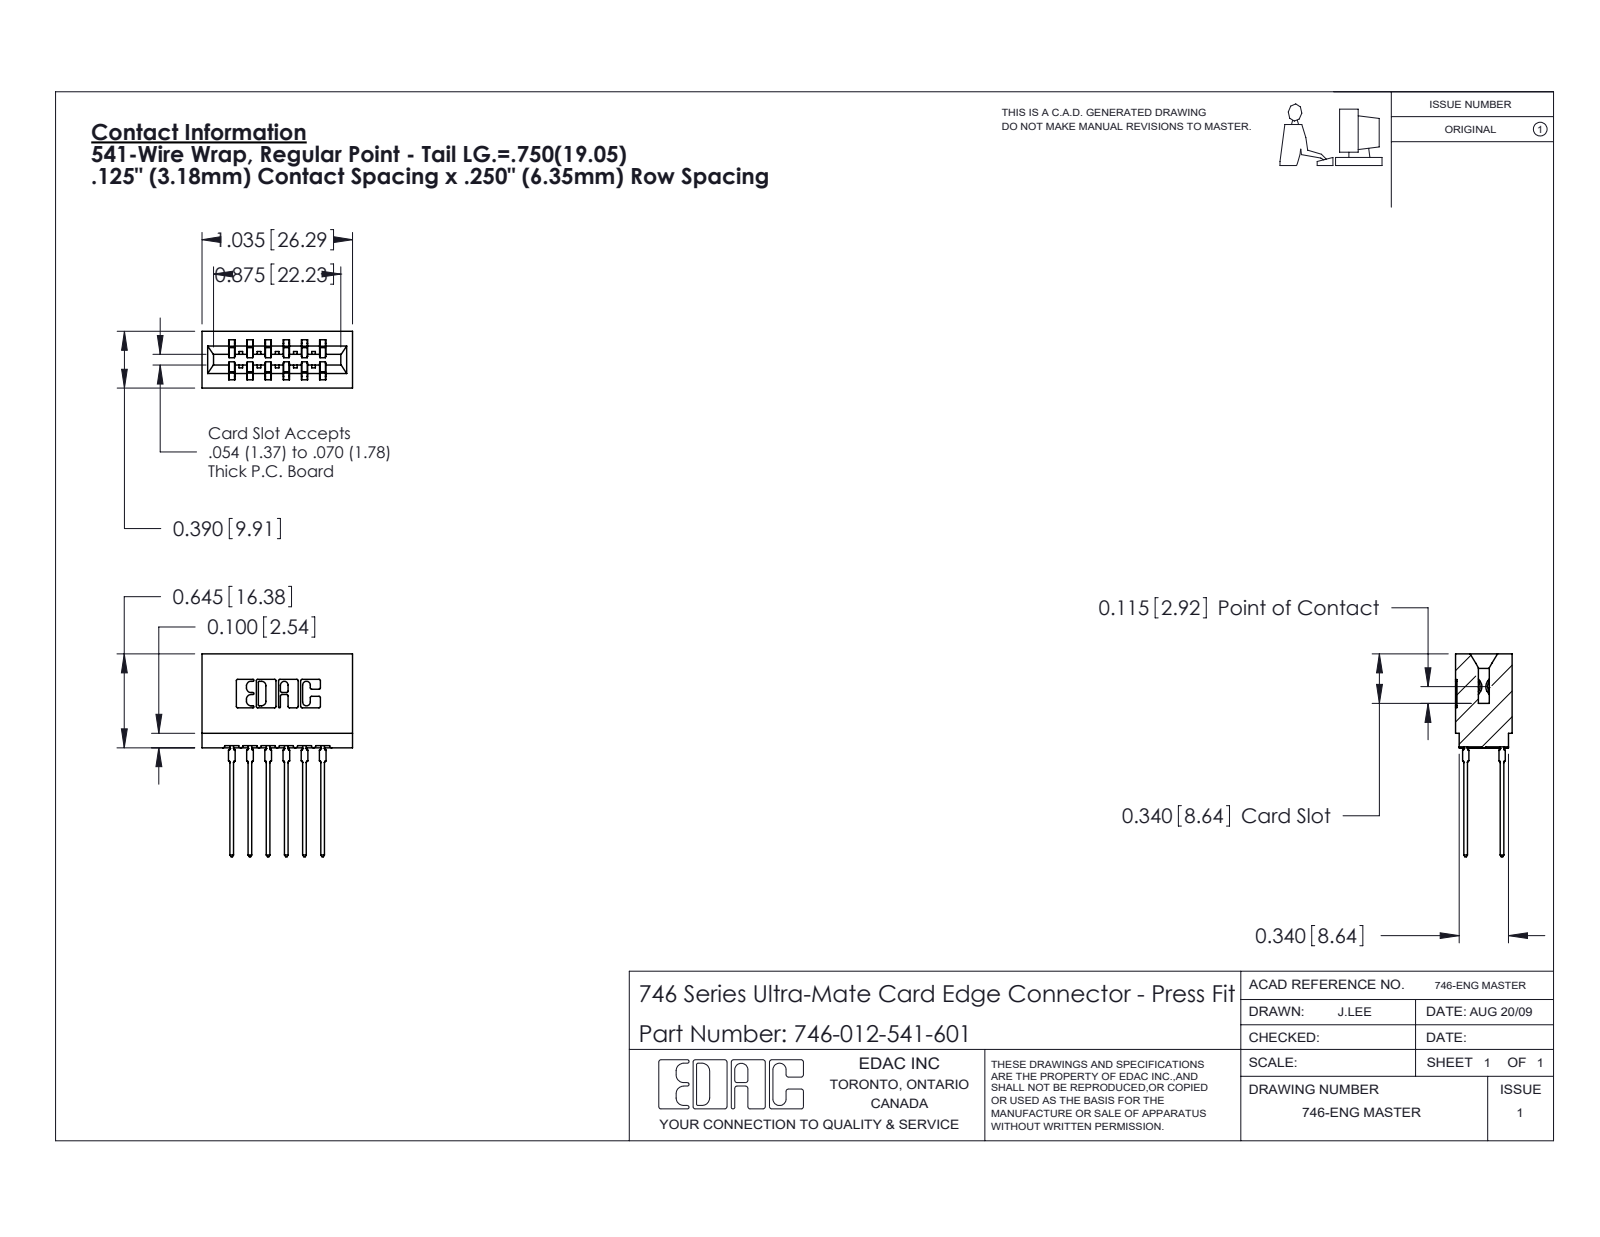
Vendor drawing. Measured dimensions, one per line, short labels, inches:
name: 746 Part_.340 Slot Depth - 01; 746-292-001_541; 746-012-541-601
written by: SolidWorks 2020 (CONFIG_CONTROL_DESIGN)
unit: in
bodies: 13 solids, 1171 faces (607 planar, 252 cylindrical, 312 other)
size: 1.394 × 1.035 × 0.39
volume: 0.201 in³; area: 6.953 in²
rounds: 24× R0.021, 22× R0.01, 8× R0.005, 8× R0.011, 7× R0.015, 6× R0.007, 6× R0.031, 3× R0.026
face distances: 0.25, 0.057, 0.333, 0.125, 0.042, 0.083, 0.375, 0.025, 0.125, 0.5
